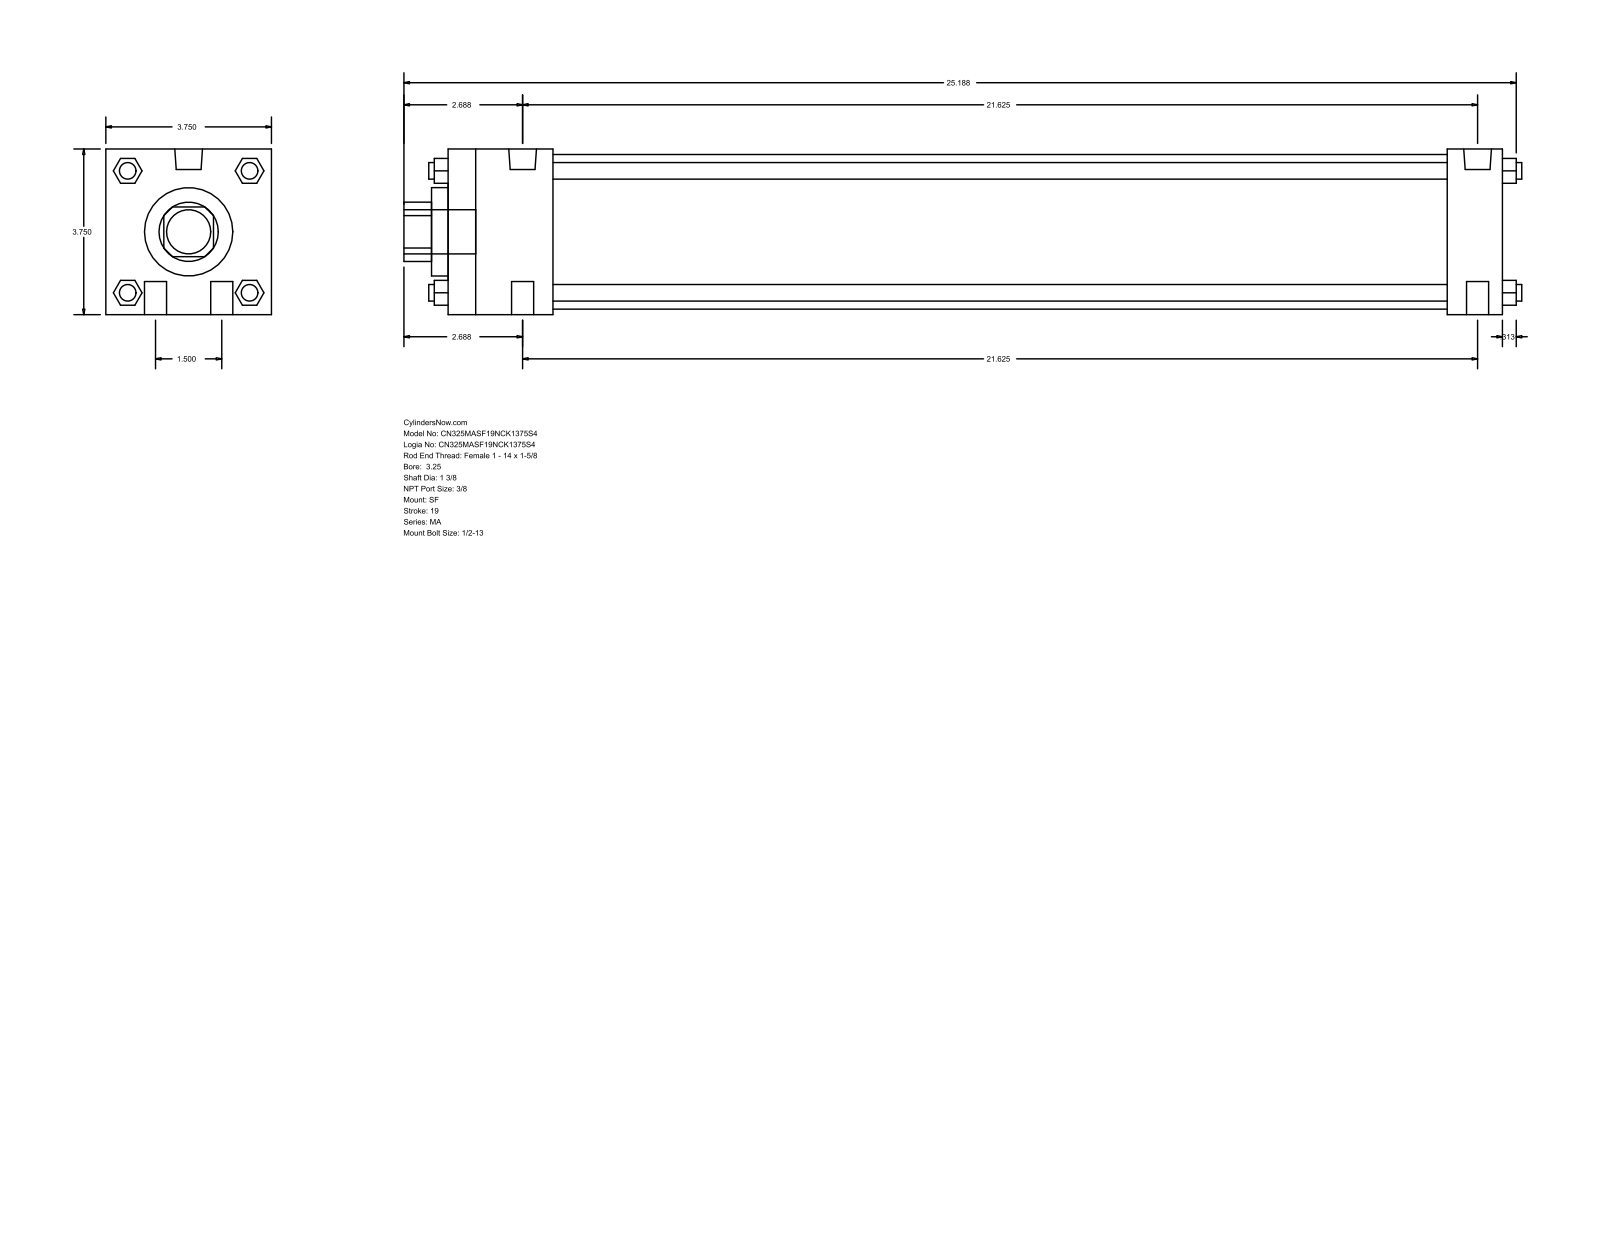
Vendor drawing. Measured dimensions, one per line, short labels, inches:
name: MA_SF__0325_1.375
written by: GSSL Pune (CONFIG_CONTROL_DESIGN)
unit: in
bodies: 0 solids, 124 faces (94 planar, 30 cylindrical, 0 other)
size: 25.313 × 3.75 × 3.75
holes: 1× ⌀1.375, 1× ⌀2, 1× ⌀3.5
bosses: 4× ⌀0.5, 4× ⌀0.375, 2× ⌀0.627, 2× ⌀0.437, 1× ⌀1
rounds: 1× R0.672
face distances: 3.75, 23.875, 22.625, 1.25, 2.375, 20.25, 21.5, 0.375, 2.75, 23
